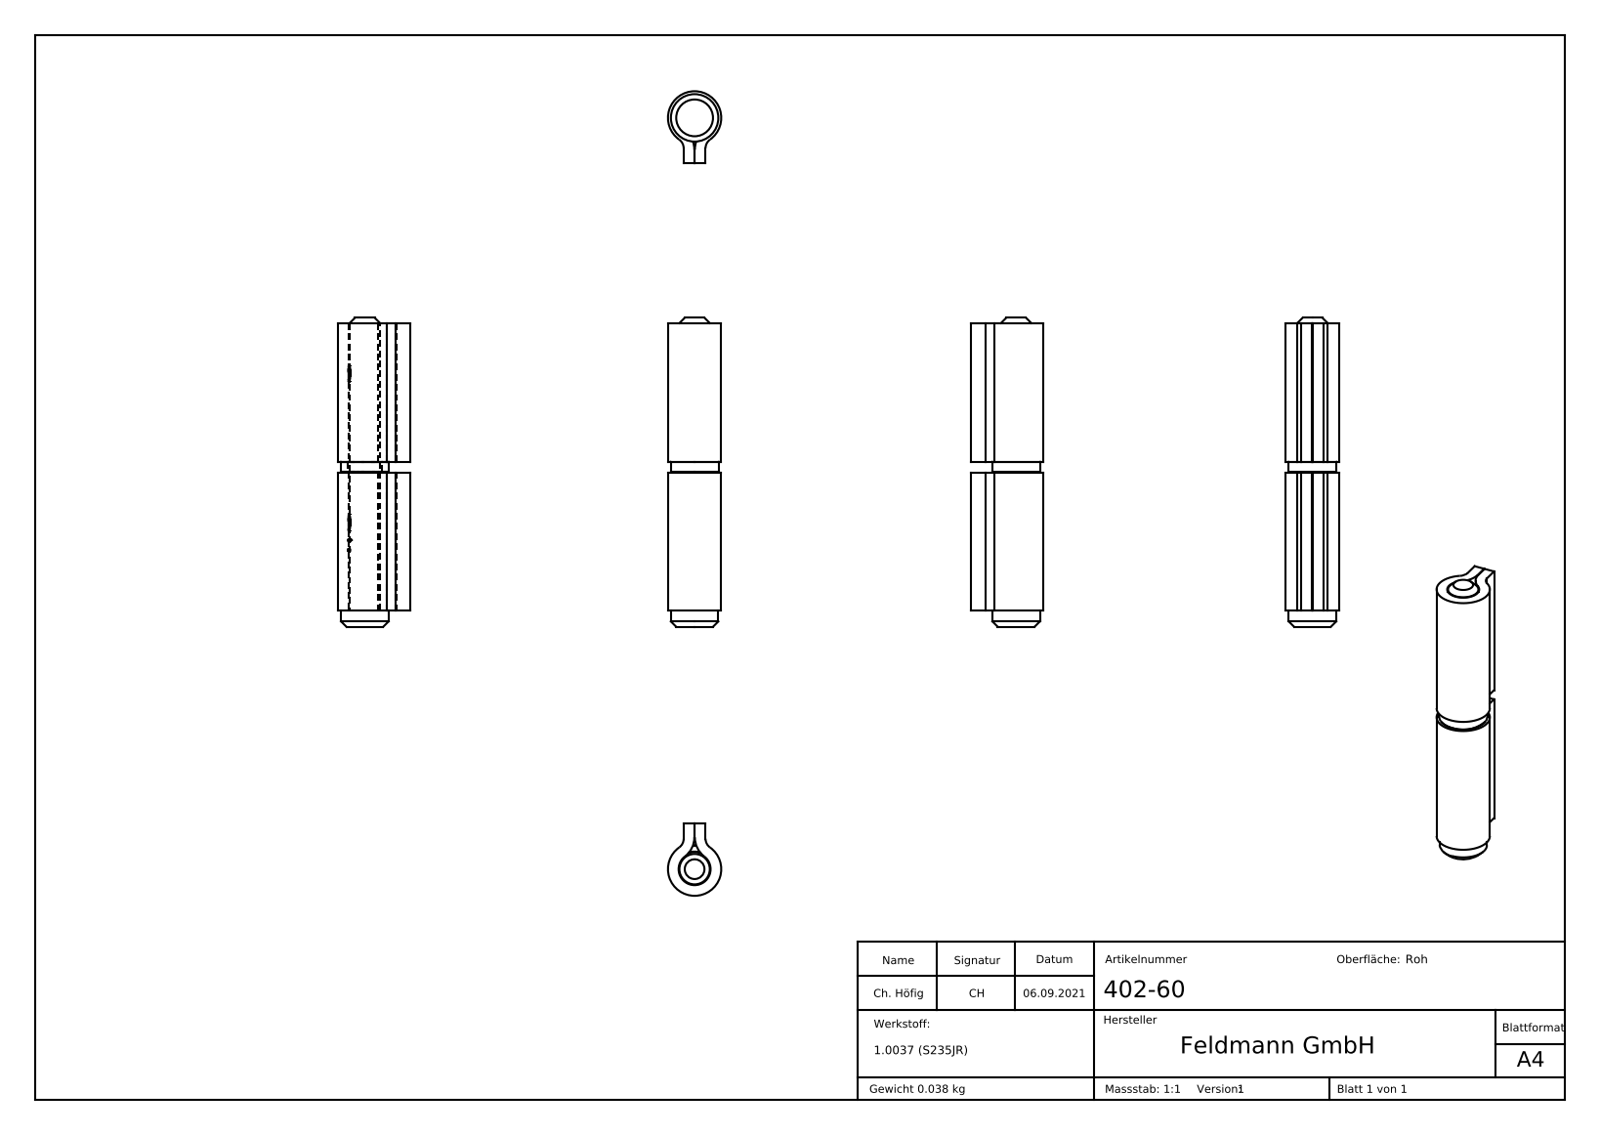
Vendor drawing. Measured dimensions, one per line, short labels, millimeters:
name: 402-xx Teil4_402-60 Teil4; 402-xx Teil3; 402-xx Teil3_402-60 Teil3; 402-xx Teil1_402-60 Teil1 (+5 more)
written by: SolidWorks 2018 (CONFIG_CONTROL_DESIGN)
unit: mm
bodies: 4 solids, 311 faces (145 planar, 39 cylindrical, 127 other)
size: 58 × 13.5 × 10
volume: 4 891 mm³; area: 5 059 mm²
holes: 1× ⌀6.4
bosses: 1× ⌀10, 1× ⌀9, 1× ⌀8.9, 1× ⌀5.7
rounds: 2× R2, 2× R4.5, 1× R3, 1× R3.1
face distances: 2, 2.1, 28, 26, 4.1, 54, 29, 3, 31, 57
